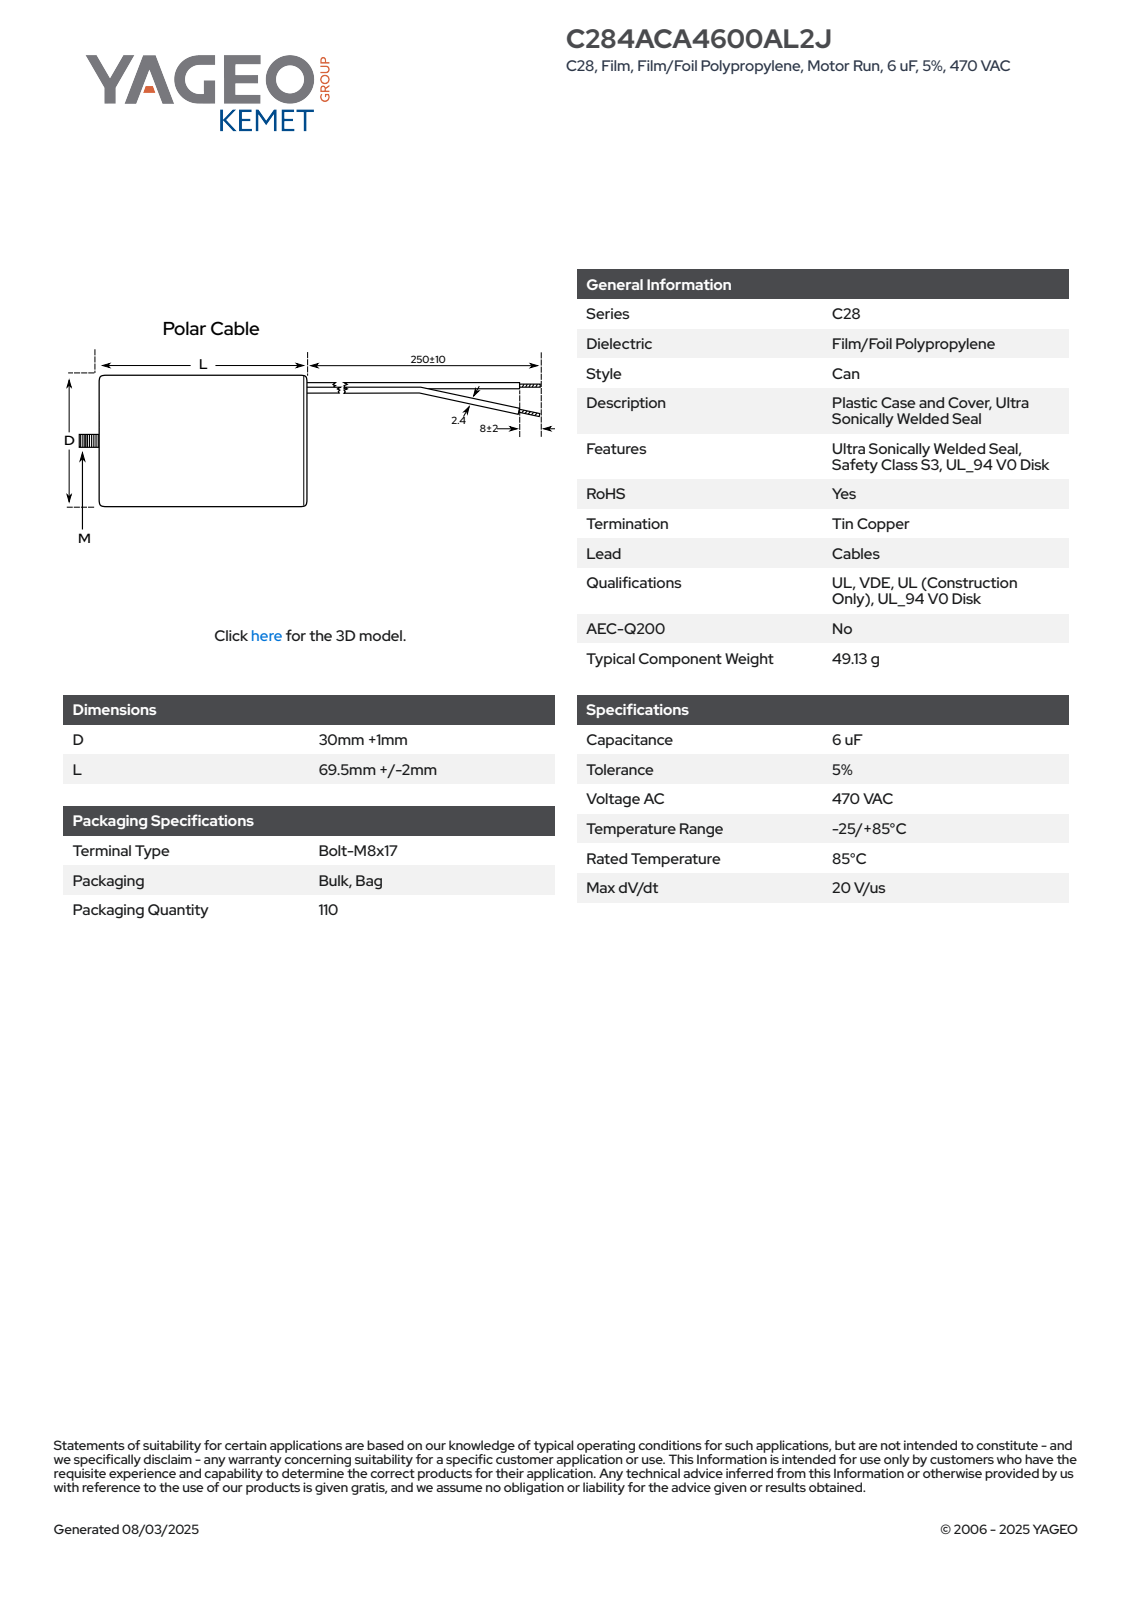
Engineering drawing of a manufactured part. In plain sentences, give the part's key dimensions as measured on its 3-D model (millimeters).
The part is named "CFM_C28P_30X69.5_D31L71.5". Its 3-D file was written by "SolidWorks 2021 (AUTOMOTIVE_DESIGN)". It is 1 solid with 76 faces: 26 planar, 15 cylindrical and 35 other. Overall it measures 81.5 by 31.01 by 31 millimeters. Its volume is 53 283 cubic millimeters and its surface area 8 811 square millimeters. Round holes: 1 of diameter 27. Round bosses or shafts: 1 of diameter 31, 1 of diameter 8. Partial cylindrical surfaces (rounded edges, fillets, slot ends): 1 of radius 15.51. The main face-to-face distances are 69.5, 71.5, 2, 10, 79.5, 81.5.
